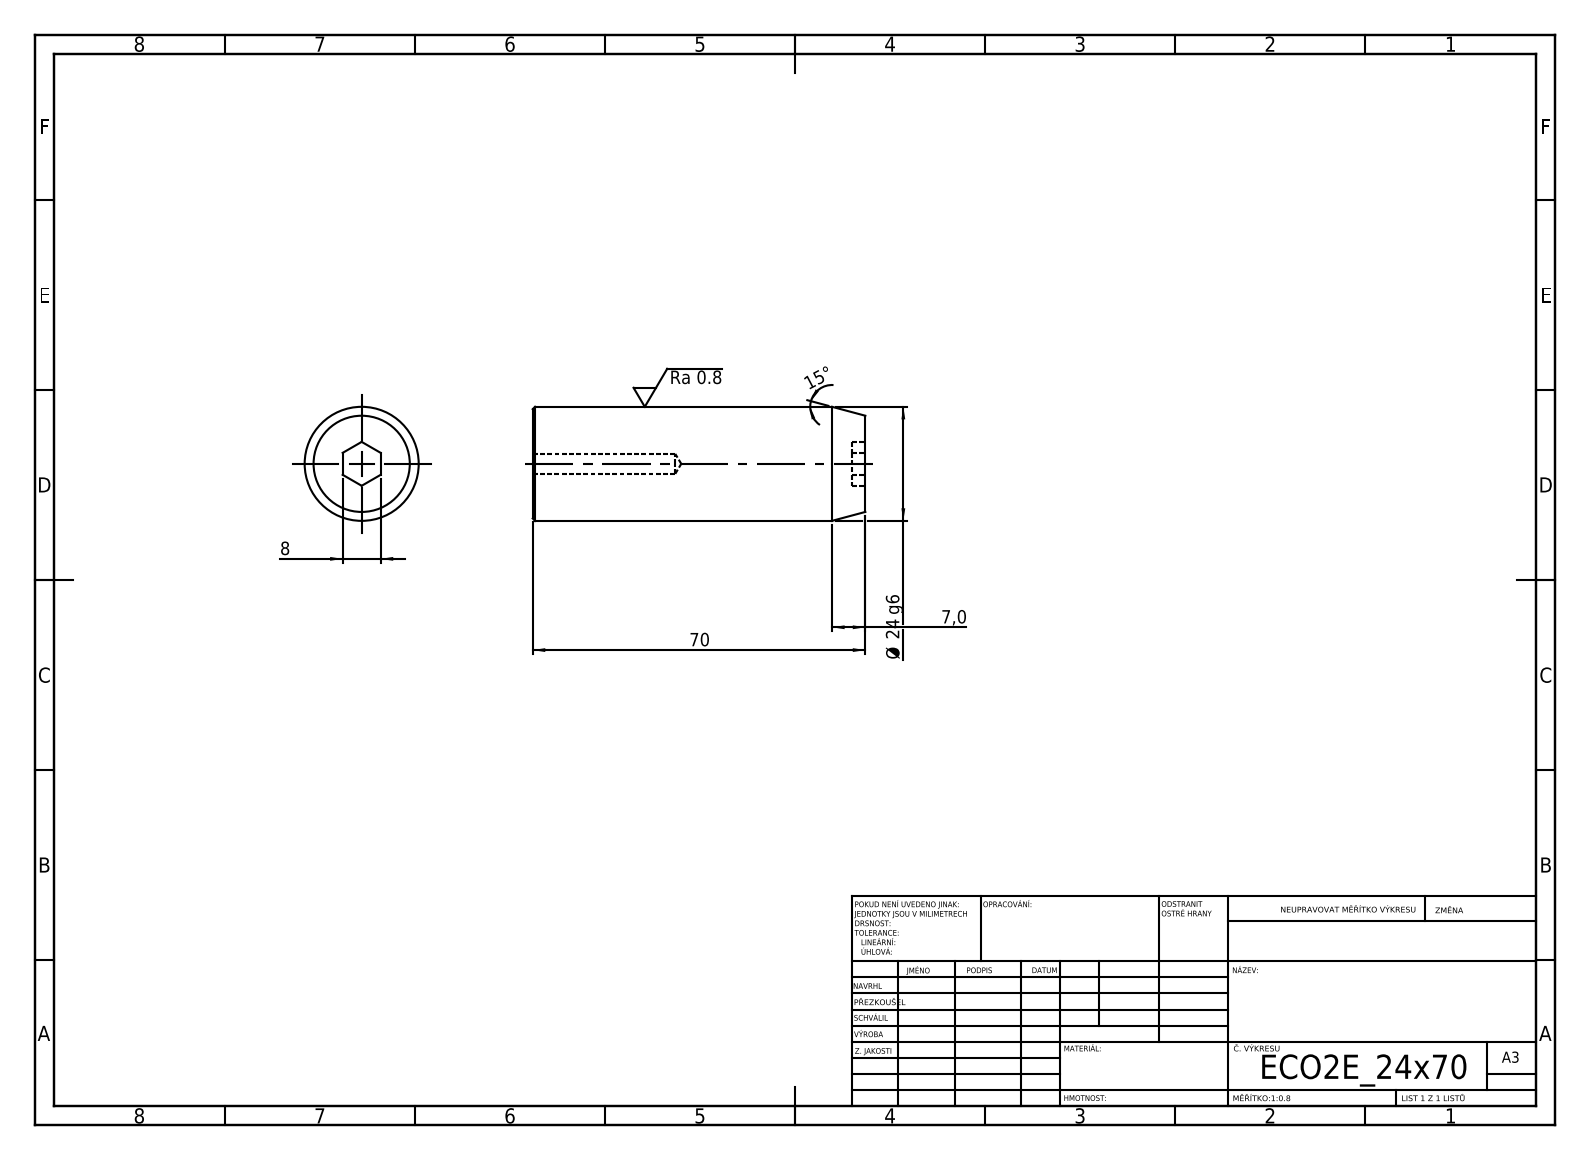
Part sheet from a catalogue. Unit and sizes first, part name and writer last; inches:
Units: inches
Overall size (bounding box): 2.756 × 0.945 × 0.945
Round holes (diameter × count): ⌀0.165 ×1
Round bosses / shafts (diameter × count): ⌀0.945 ×1
Main face-to-face distances: 2.756, 0.11, 2.646, 0.315
Volume: 1.868 in³ · Surface area: 10.05 in²
Bodies: 1 solid, 19 faces (9 planar, 4 cylindrical, 6 other)
STEP written by: SolidWorks 2019 (CONFIG_CONTROL_DESIGN)
